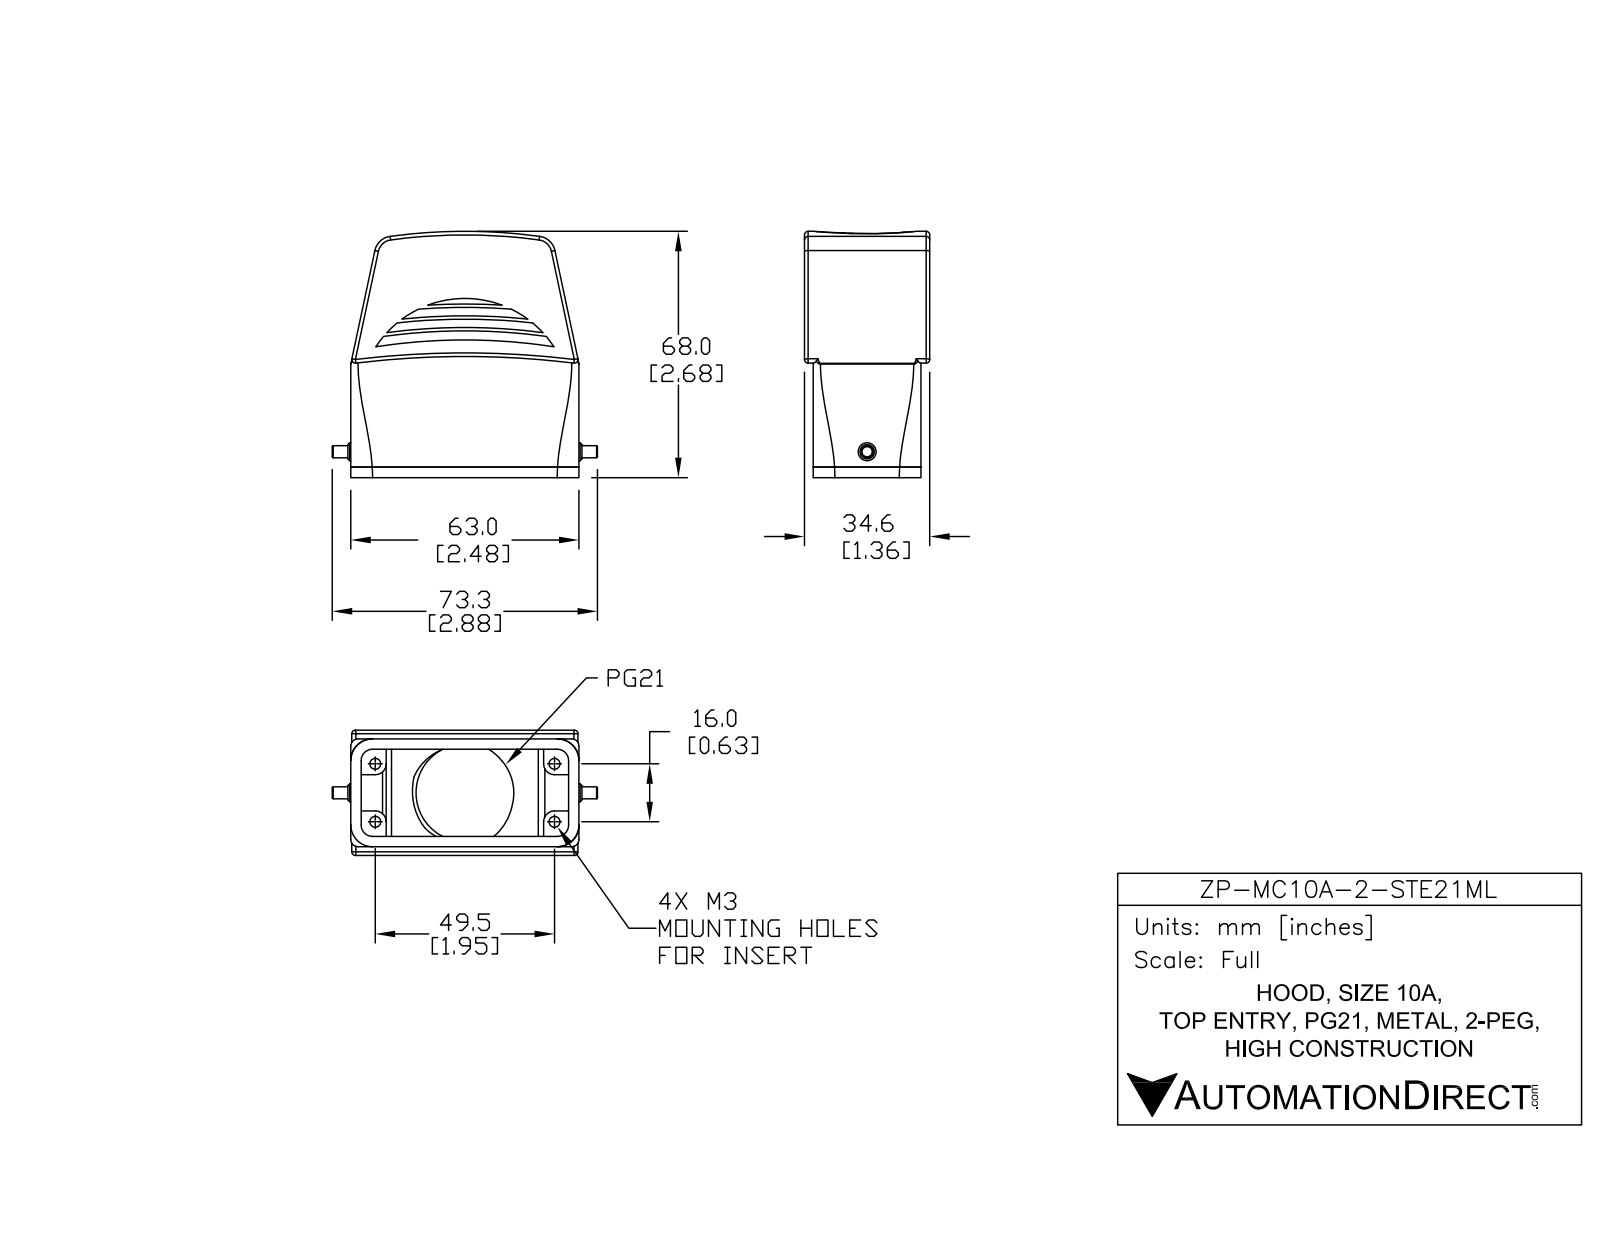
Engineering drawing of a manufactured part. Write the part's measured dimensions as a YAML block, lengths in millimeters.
part_name: "ZP-MC10A-2-STE21ML"
step_written_by: "SolidWorks 2014 (AUTOMOTIVE_DESIGN)"
units: millimeters
bodies: {solids: 2, faces: 222, planar: 54, cylindrical: 96, other: 72}
overall_size: [73.25, 68.3, 34.6]
volume: 48453
surface_area: 26369
round_holes:
  - {diameter: 3, count: 4}
  - {diameter: 27, count: 1}
round_bosses_or_shafts:
  - {diameter: 4.95, count: 1}
  - {diameter: 3.33, count: 1}
partial_cylinders:
  - {radius: 1, count: 9}
  - {radius: 3, count: 4}
  - {radius: 2.15, count: 2}
  - {radius: 5, count: 2}
  - {radius: 29.32, count: 1}
  - {radius: 150.6, count: 1}
  - {radius: 153.45, count: 1}
  - {radius: 161.93, count: 1}
face_to_face_distances: [2.85, 26.93, 2.41, 5.26, 29.34, 32.19, 24.08, 29.78, 34.6, 53.25]
hole_center_spacings: [26.01, 16, 49.5, 52.02]
